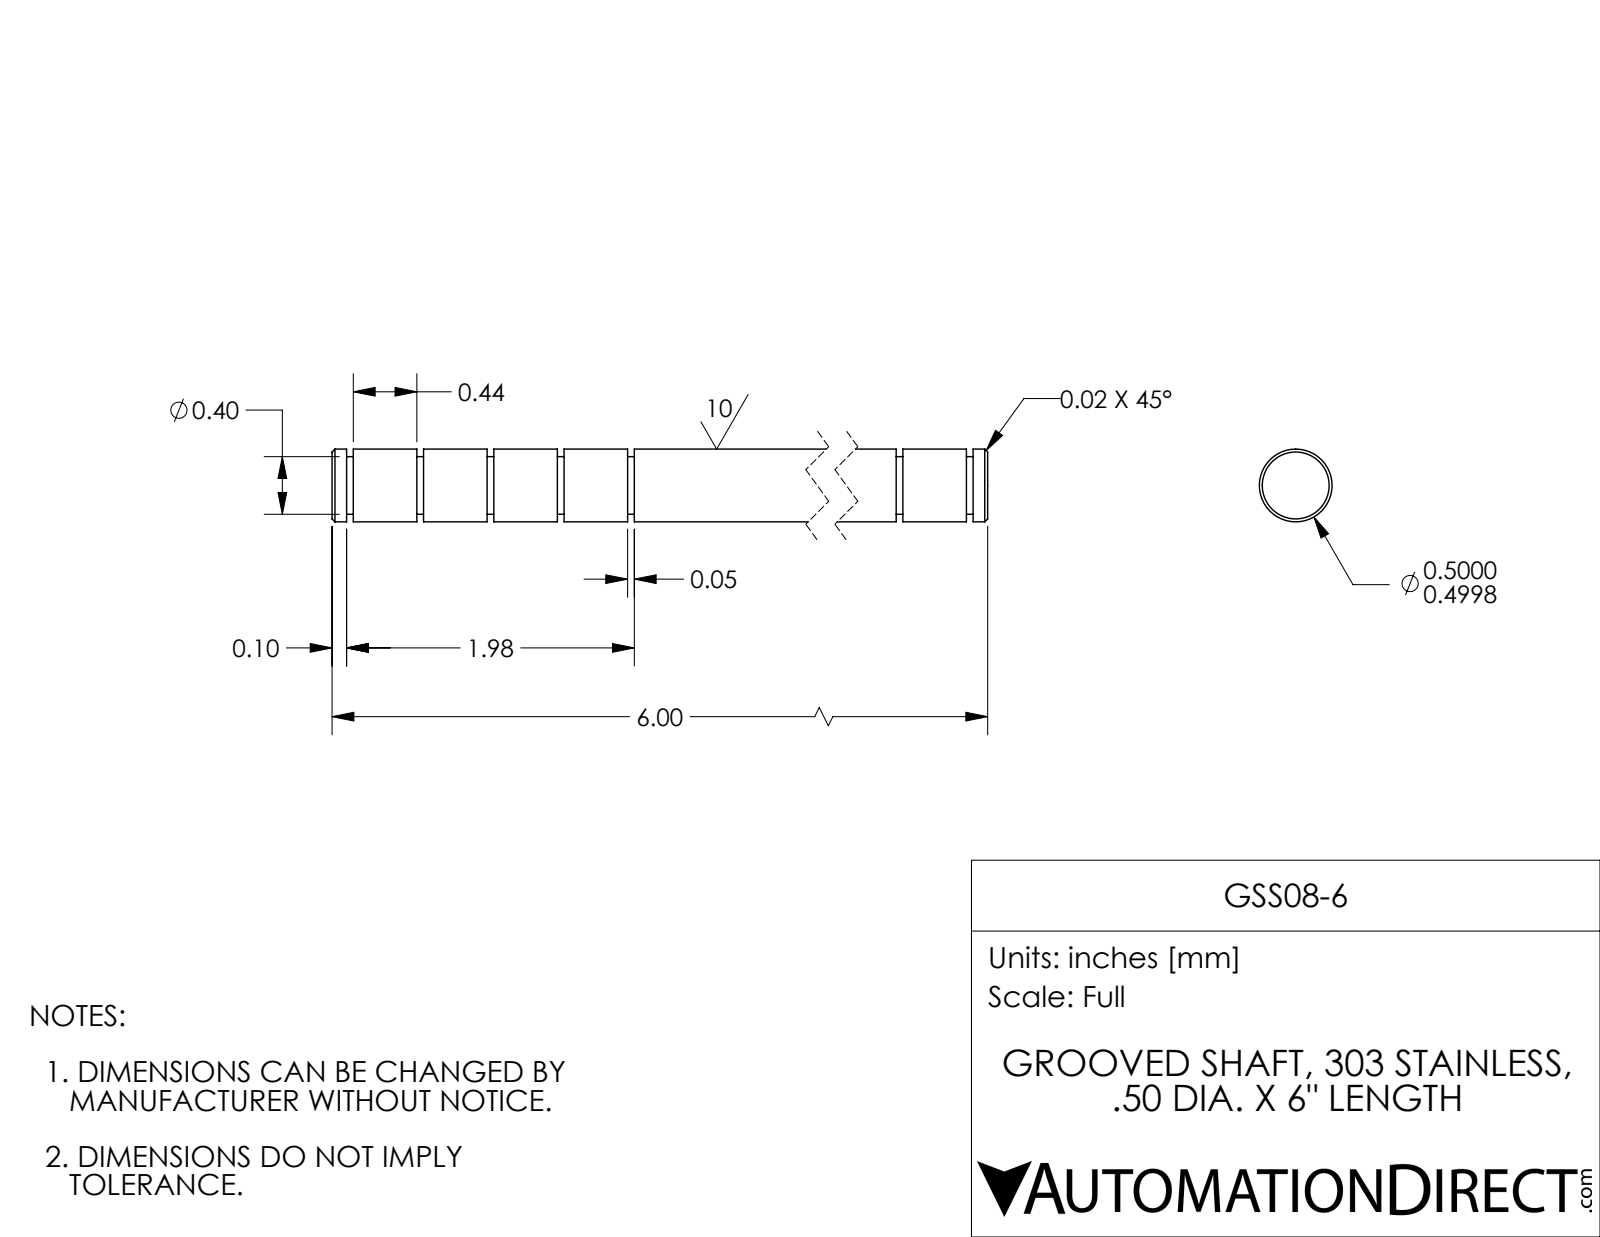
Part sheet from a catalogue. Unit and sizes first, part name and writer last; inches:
Units: inches
Overall size (bounding box): 6 × 0.5 × 0.5
Round bosses / shafts (diameter × count): ⌀0.5 ×1, ⌀0.396 ×1
Main face-to-face distances: 0.483, 0.046, 0.437, 1.449, 5.271, 3.822, 0.966, 0.529, 1.012, 4.788
Volume: 1.154 in³ · Surface area: 10.7 in²
Bodies: 1 solid, 50 faces (16 planar, 30 cylindrical, 4 other)
Part name (STEP PRODUCT): GSS08-6
STEP written by: SolidWorks 2017 (AUTOMOTIVE_DESIGN)
